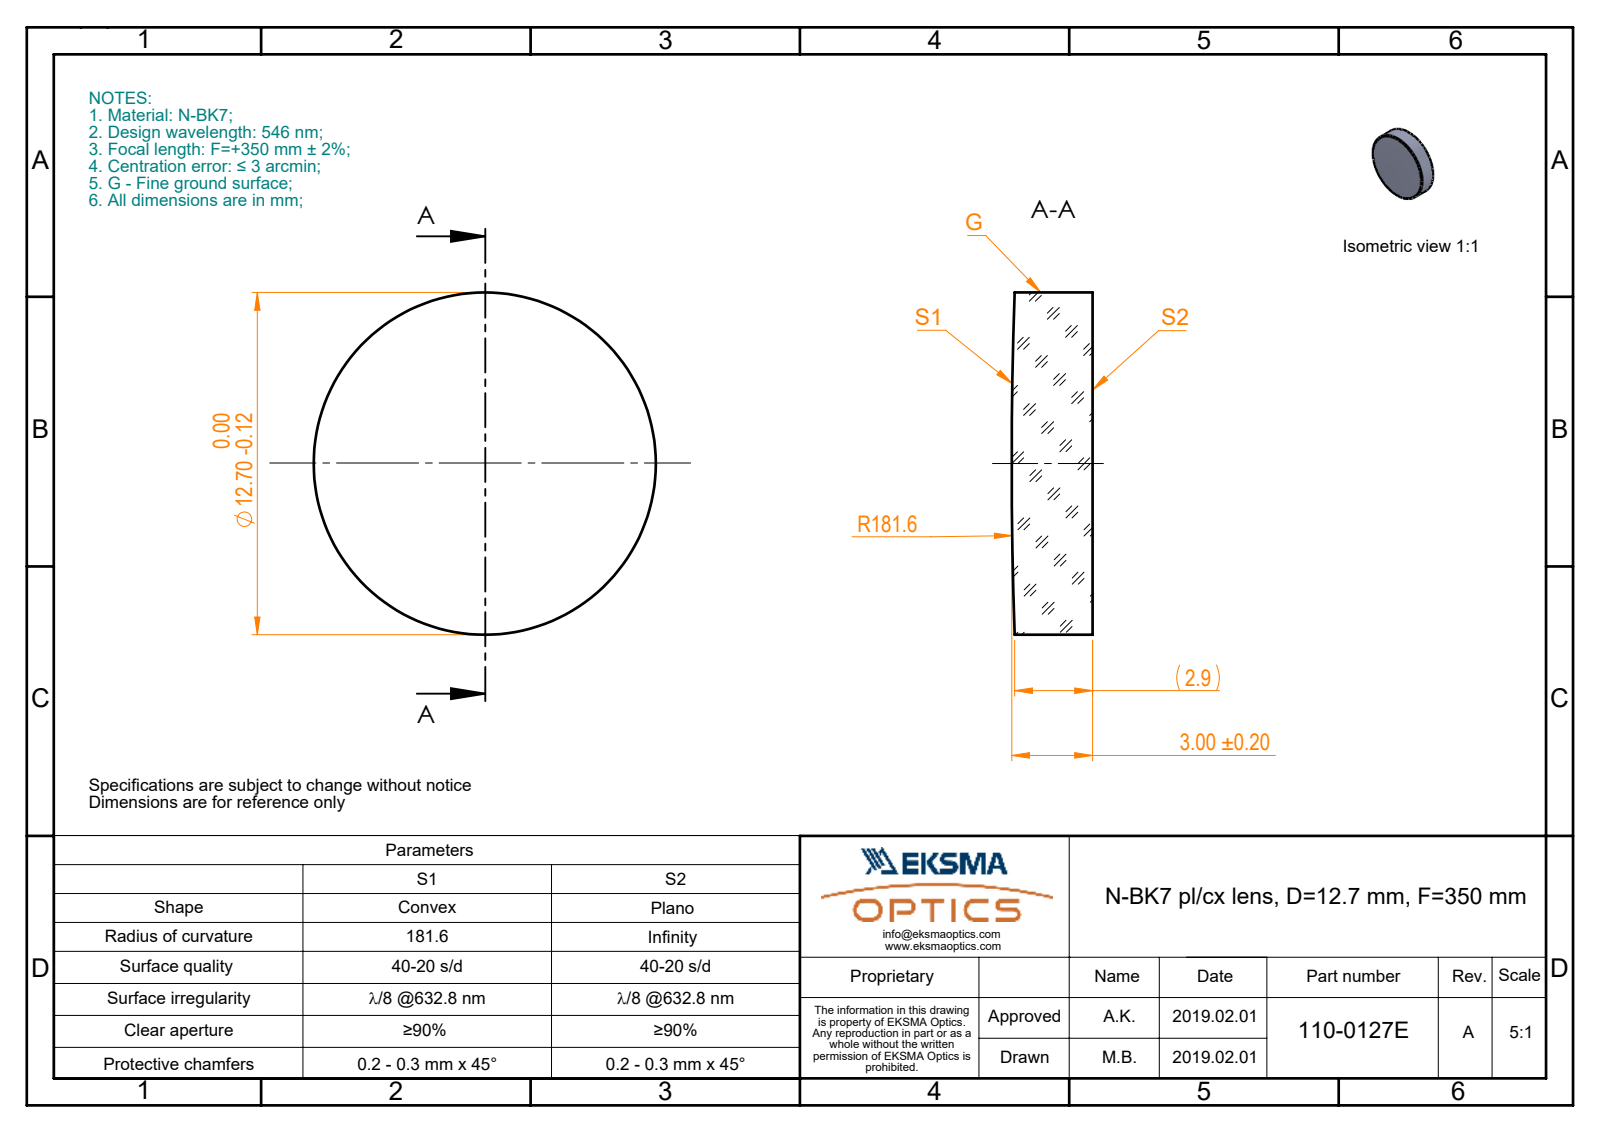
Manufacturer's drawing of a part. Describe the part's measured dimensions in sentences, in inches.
The part is named "110-0127E BK7 pl-cx 12.7 F350". Its 3-D file was written by "SolidWorks 2017 (CONFIG_CONTROL_DESIGN)". It is 1 solid with 5 faces: 1 planar, 2 cylindrical and 2 other. Overall it measures 0.5 by 0.5 by 0.118 inches. Its volume is 0.023 cubic inches and its surface area 0.572 square inches. Round bosses or shafts: 1 of diameter 0.5.
